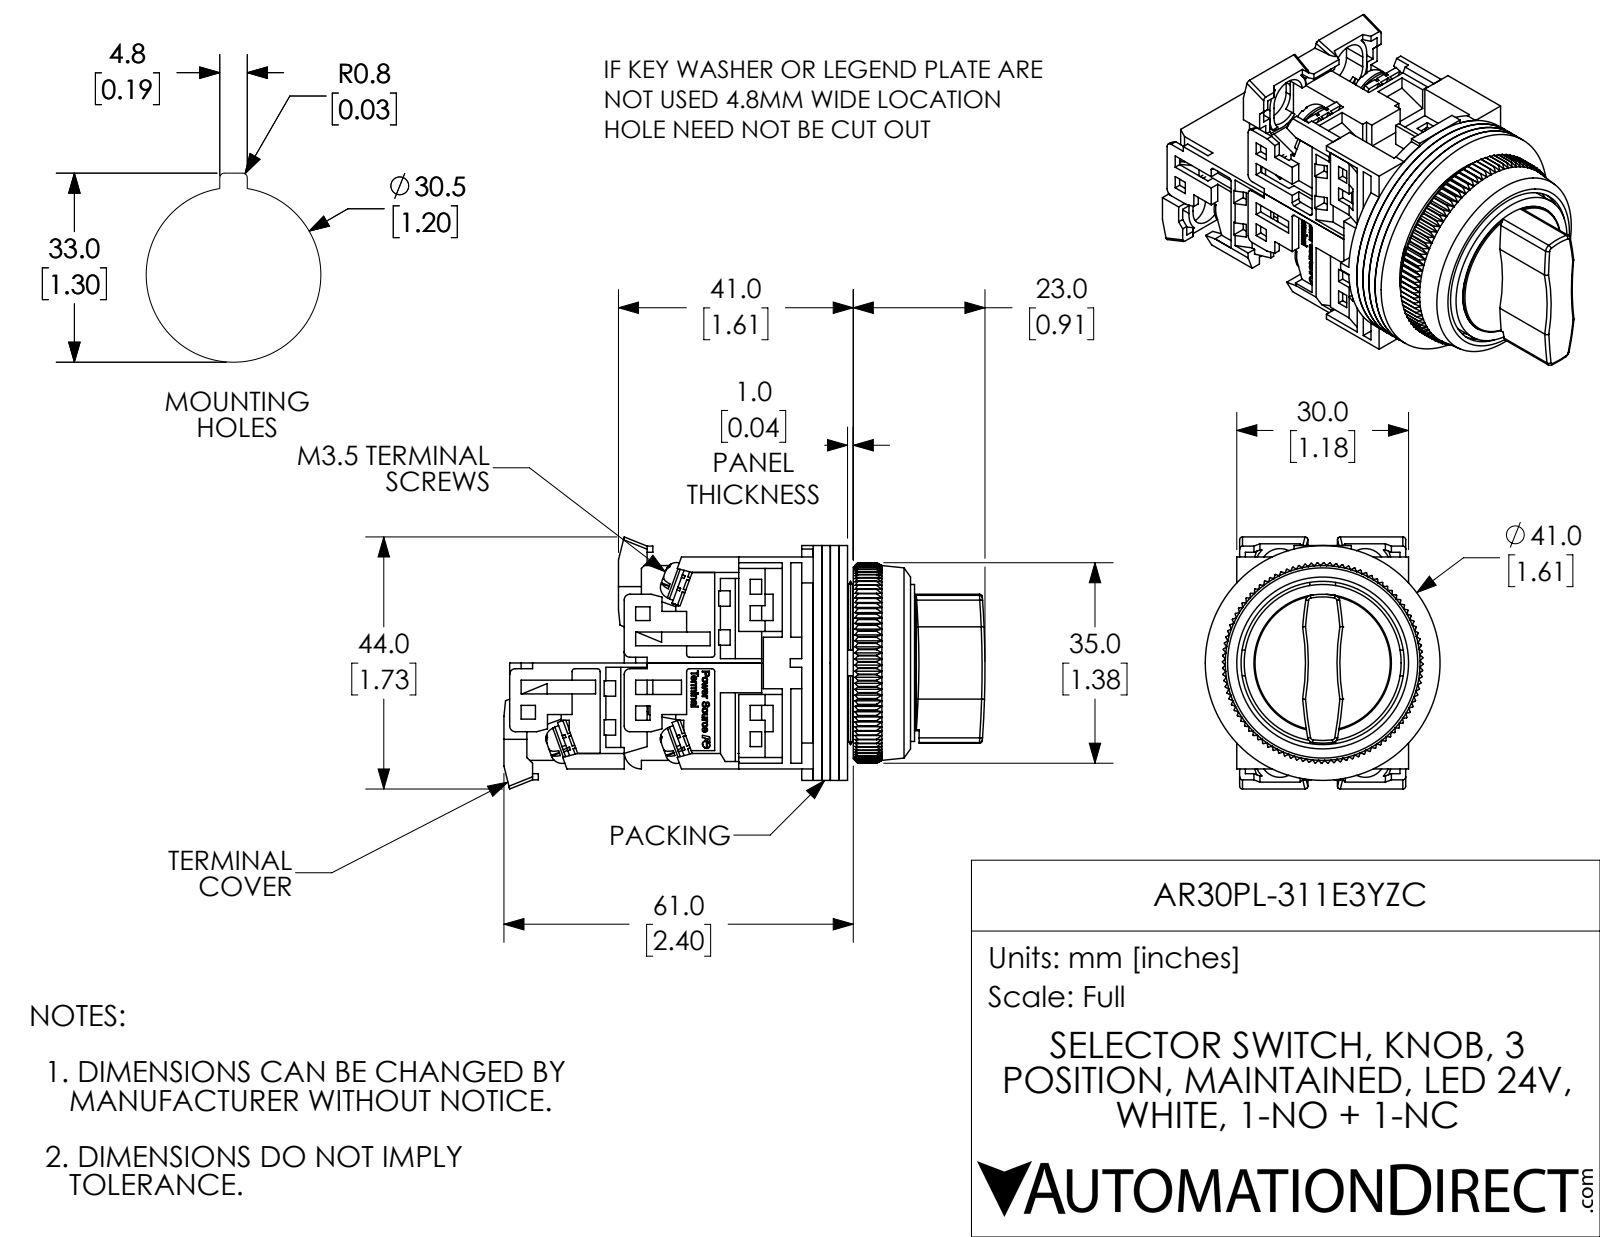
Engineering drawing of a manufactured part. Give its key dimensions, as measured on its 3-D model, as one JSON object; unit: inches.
{"part_name": "AR30PL-311E3YZC", "step_written_by": "SolidWorks 2017 (AUTOMOTIVE_DESIGN)", "units": "inches", "bodies": {"solids": 32, "faces": 2783, "planar": 2039, "cylindrical": 338, "other": 406}, "overall_size": [3.307, 1.732, 1.614], "volume_in3": 2.677, "surface_area_in2": 66.54, "round_holes": [[0.138, 10], [0.142, 6], [0.118, 1], [0.472, 1], [0.709, 1], [0.768, 1], [0.827, 1], [1.122, 1], [1.181, 1], [1.252, 1]], "round_bosses_or_shafts": [[0.26, 6], [0.138, 6], [0.063, 2], [1.614, 1], [1.15, 1], [1.079, 1], [0.945, 1], [0.886, 1]], "partial_cylinders_radius": [[0.059, 24], [0.02, 14], [0.039, 10], [0.138, 4], [0.177, 4], [0.118, 3], [1.575, 2], [2.953, 2]], "face_to_face_distances": [0.059, 0.118, 0.177, 0.039, 0.787, 0.063, 0.079, 0.02, 0.811, 0.689], "hole_center_spacings": [0.579, 0.269, 0.638, 0.61]}
